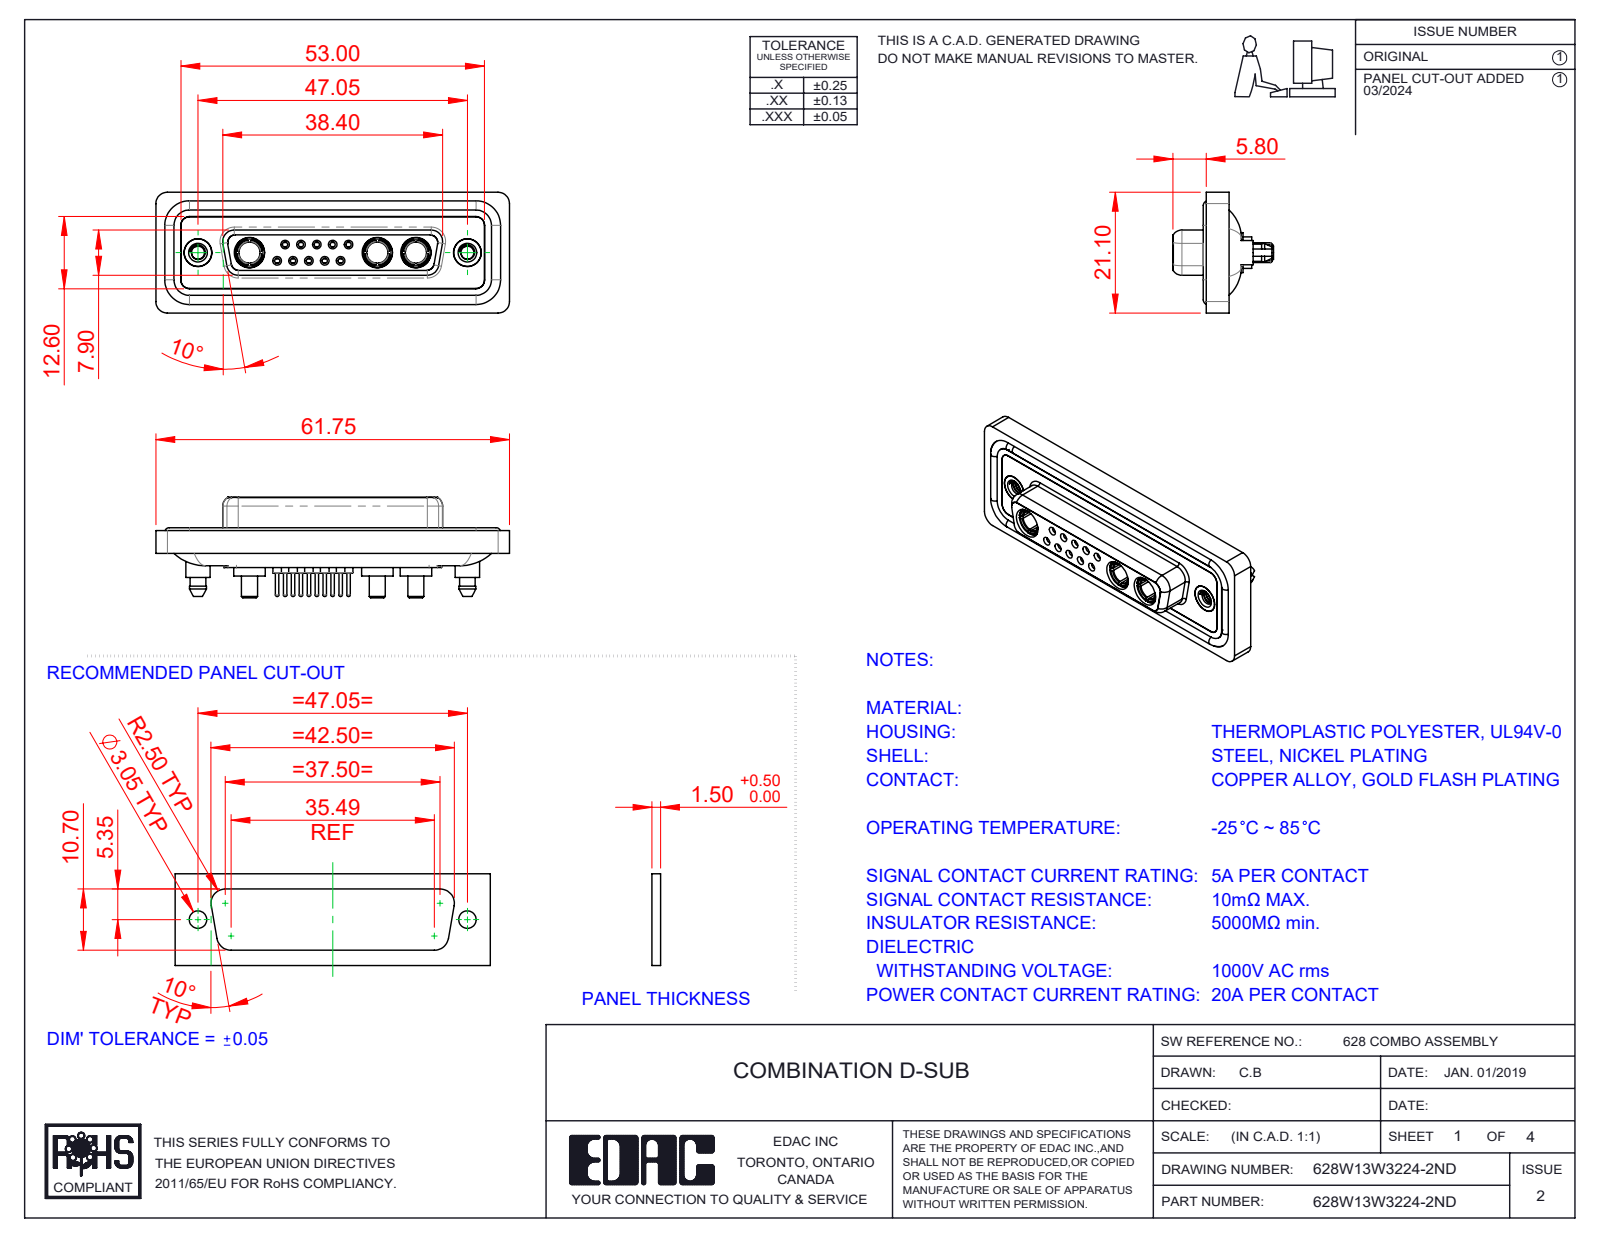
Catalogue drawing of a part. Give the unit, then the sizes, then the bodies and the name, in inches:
Units: inches
Overall size (bounding box): 2.431 × 0.831 × 0.691
Round holes (diameter × count): ⌀0.035 ×10, ⌀0.043 ×10, ⌀0.059 ×10, ⌀0.079 ×10, ⌀0.063 ×5, ⌀0.067 ×5, ⌀0.191 ×5, ⌀0.146 ×3, ⌀0.209 ×3, ⌀0.089 ×2, ⌀0.157 ×2, ⌀0.159 ×2
Round bosses / shafts (diameter × count): ⌀0.087 ×10, ⌀0.024 ×10, ⌀0.063 ×9, ⌀0.217 ×3, ⌀0.205 ×3, ⌀0.195 ×3, ⌀0.187 ×3, ⌀0.148 ×3
Partial cylindrical surfaces — rounded edges, fillets, slot ends (radius × count): R0.059 ×24, R0.079 ×18, R0.063 ×10, R0.053 ×8, R0.01 ×4, R0.02 ×4, R0.024 ×4, R0.026 ×4
Main face-to-face distances: 0.016, 0.071, 0.293, 0.222, 0.02, 0.26, 0.278, 0.063, 0.114, 0.043
Hole centre spacings: 0.124, 0.109, 0.198, 0.198, 0.218, 0.327, 0.295, 0.109
Volume: 0.513 in³ · Surface area: 21.77 in²
Bodies: 23 solids, 1224 faces (358 planar, 495 cylindrical, 371 other)
Part name (STEP PRODUCT): 628Combo Contact Row 1_24; 628Combo Shell Rear_25 Contacts; 628Combo Shell Front_25 Contacts; Power Socket_20A S (+5 more)
STEP written by: SolidWorks 2023 (CONFIG_CONTROL_DESIGN)
